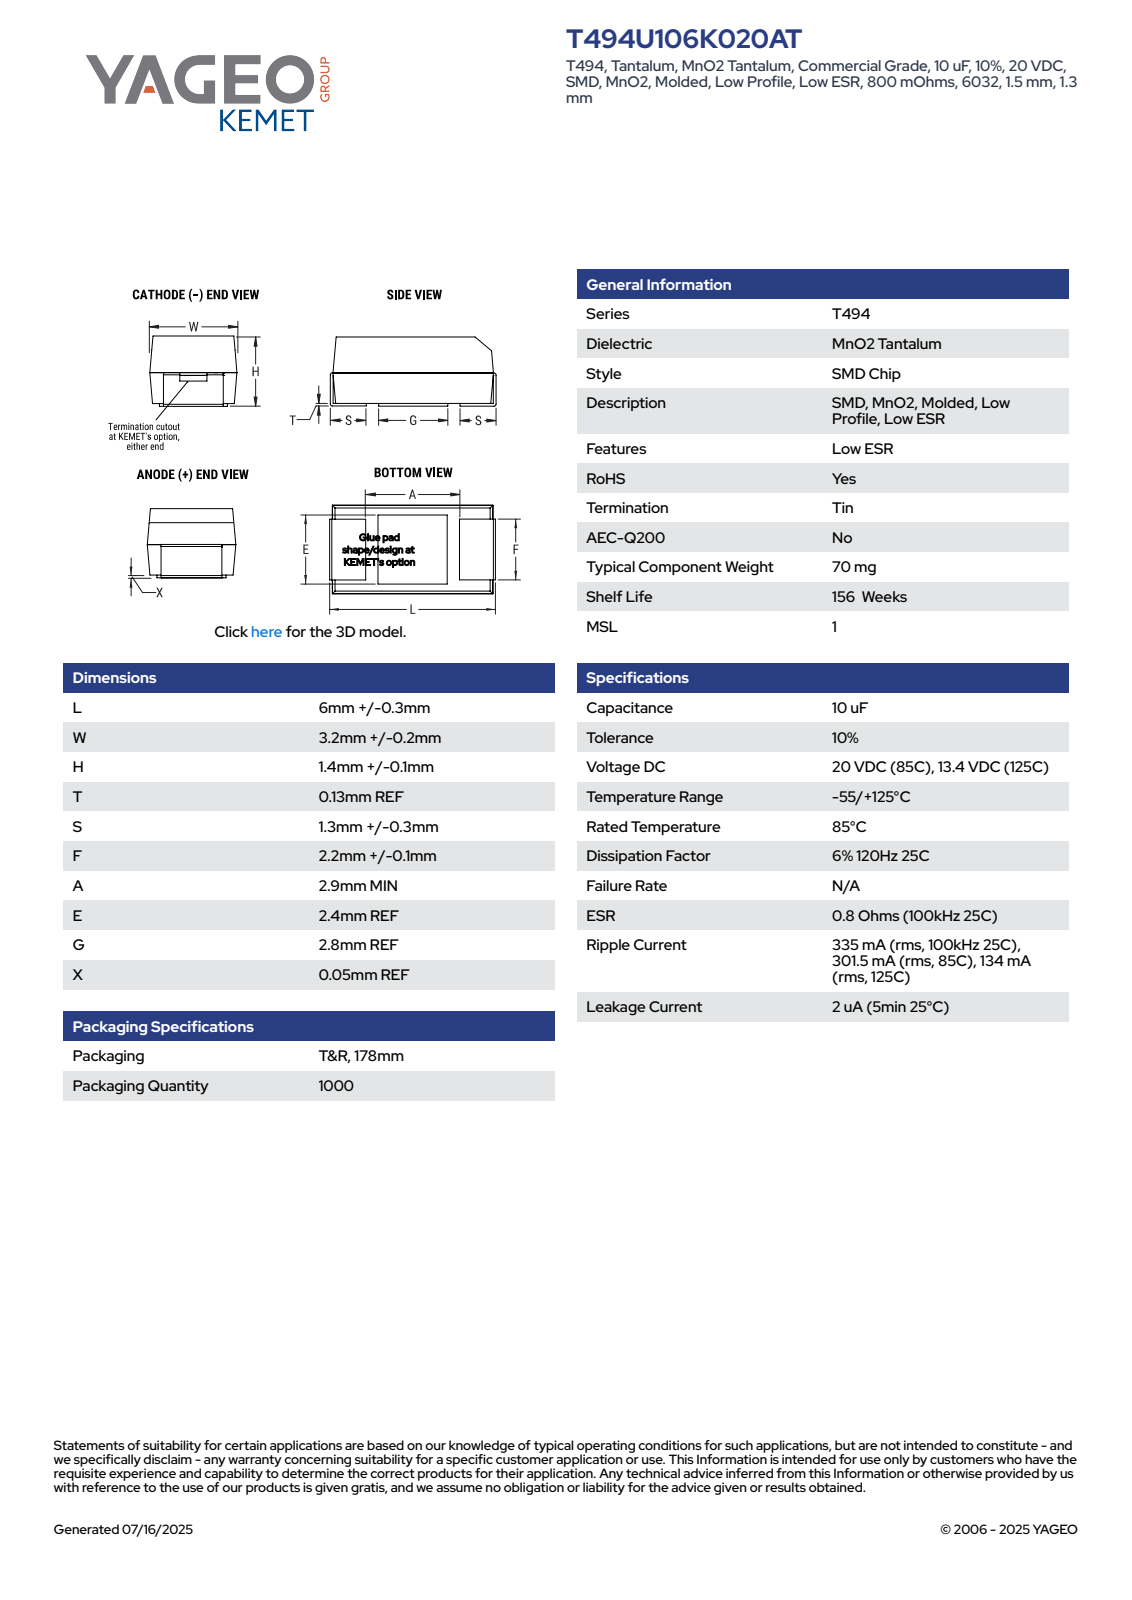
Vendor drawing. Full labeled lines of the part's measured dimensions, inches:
Part name (STEP PRODUCT): CTSM_TCM2NBKRP_6032_L6.3W3.4H1.5T0.13S1.3F2.3A2.9E2.4G2.8X0.05
STEP written by: SolidWorks 2020 (AUTOMOTIVE_DESIGN)
Units: inches
Bodies: 4 solids, 94 faces (90 planar, 4 cylindrical, 0 other)
Overall size (bounding box): 0.248 × 0.134 × 0.059
Volume: 0.002 in³ · Surface area: 0.11 in²
Partial cylindrical surfaces — rounded edges, fillets, slot ends (radius × count): R0.004 ×4
Main face-to-face distances: 0.059, 0.13, 0.057, 0.243, 0.248, 0.238, 0.054, 0.091, 0.069, 0.179
